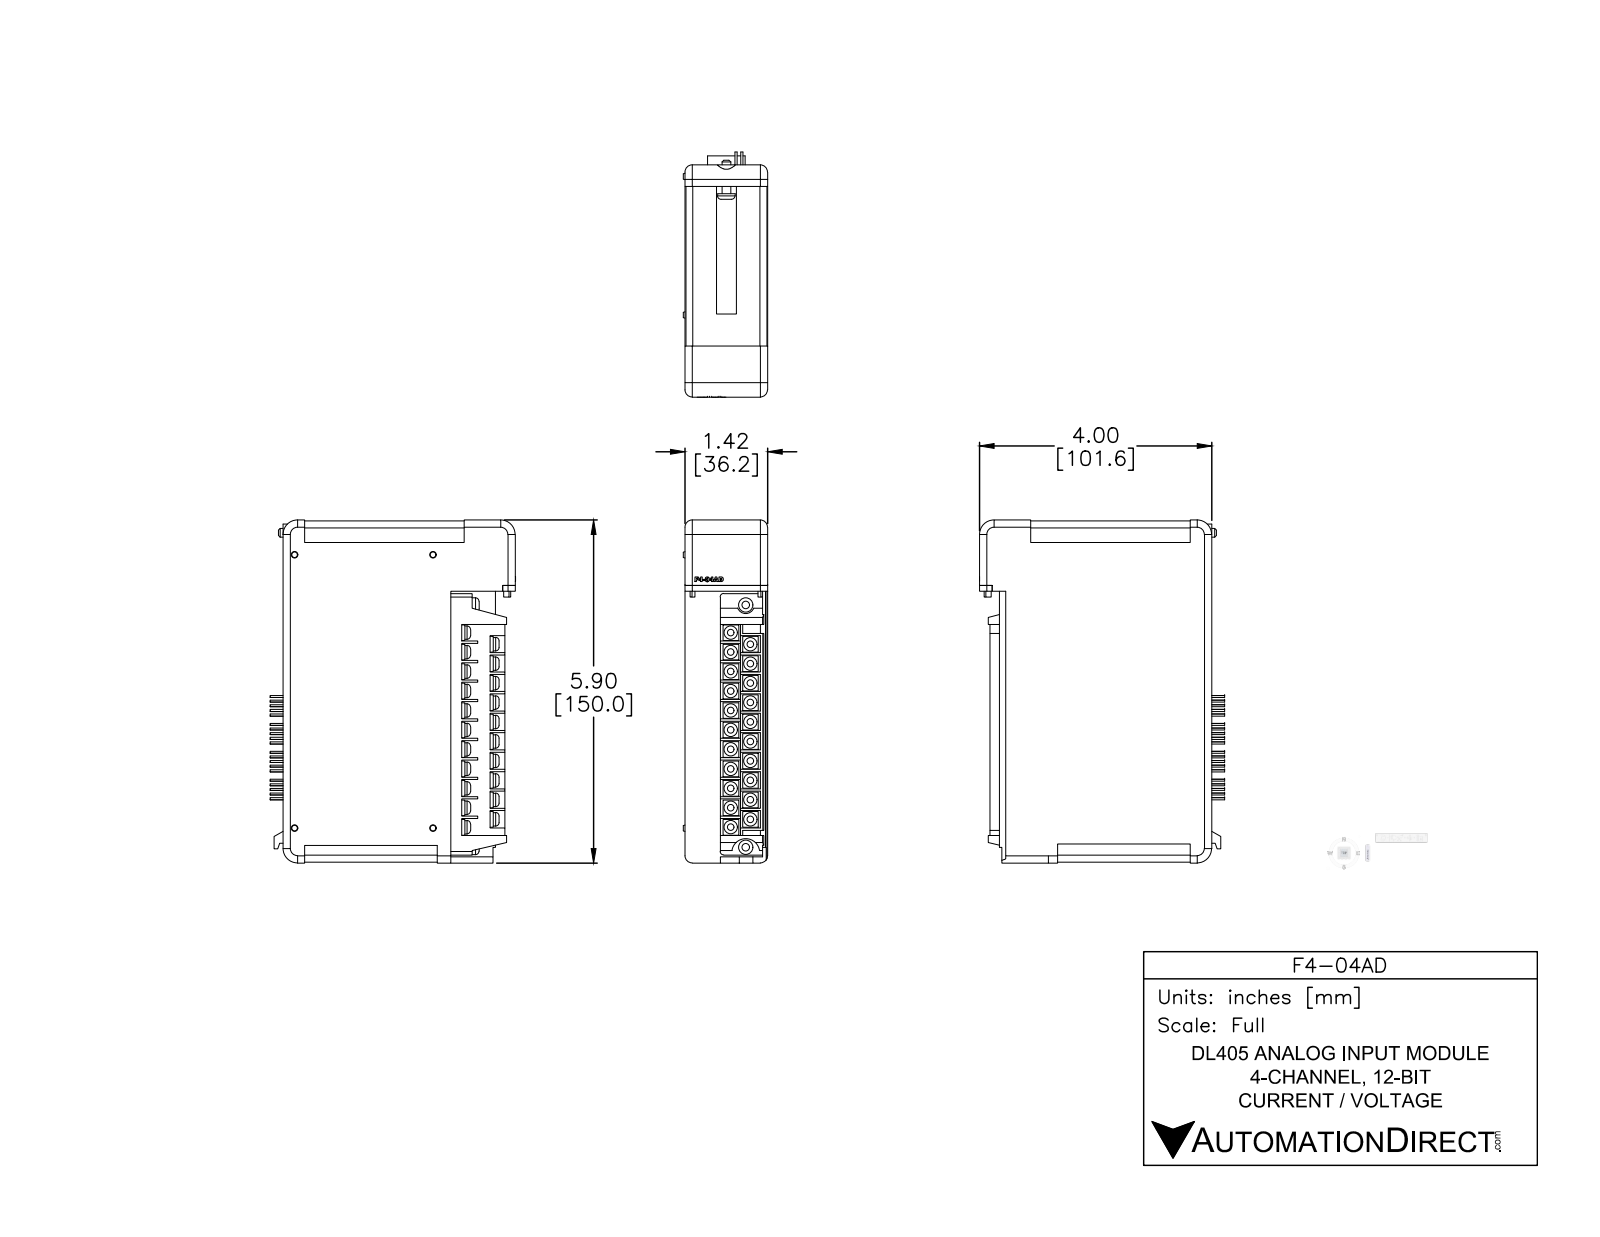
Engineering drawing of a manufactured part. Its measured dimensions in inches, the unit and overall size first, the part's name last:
Units: inches
Overall size (bounding box): 5.905 × 4.223 × 1.455
Round bosses / shafts (diameter × count): ⌀0.23 ×21, ⌀0.035 ×20, ⌀0.035 ×20, ⌀0.25 ×2, ⌀0.3 ×1, ⌀0.15 ×1
Partial cylindrical surfaces — rounded edges, fillets, slot ends (radius × count): R0.015 ×82, R0.125 ×8, R0.12 ×4, R0.25 ×3, R0.03 ×2, R0.06 ×2, R0.149 ×1, R0.151 ×1
Main face-to-face distances: 1.425, 0.015, 2.89, 5.875, 1.41, 0.47, 0.955, 5.89, 1.21, 0.345
Volume: 27.6 in³ · Surface area: 90.48 in²
Bodies: 6 solids, 881 faces (557 planar, 246 cylindrical, 78 other)
Part name (STEP PRODUCT): F4-04AD
STEP written by: SolidWorks 2014 (AUTOMOTIVE_DESIGN)
